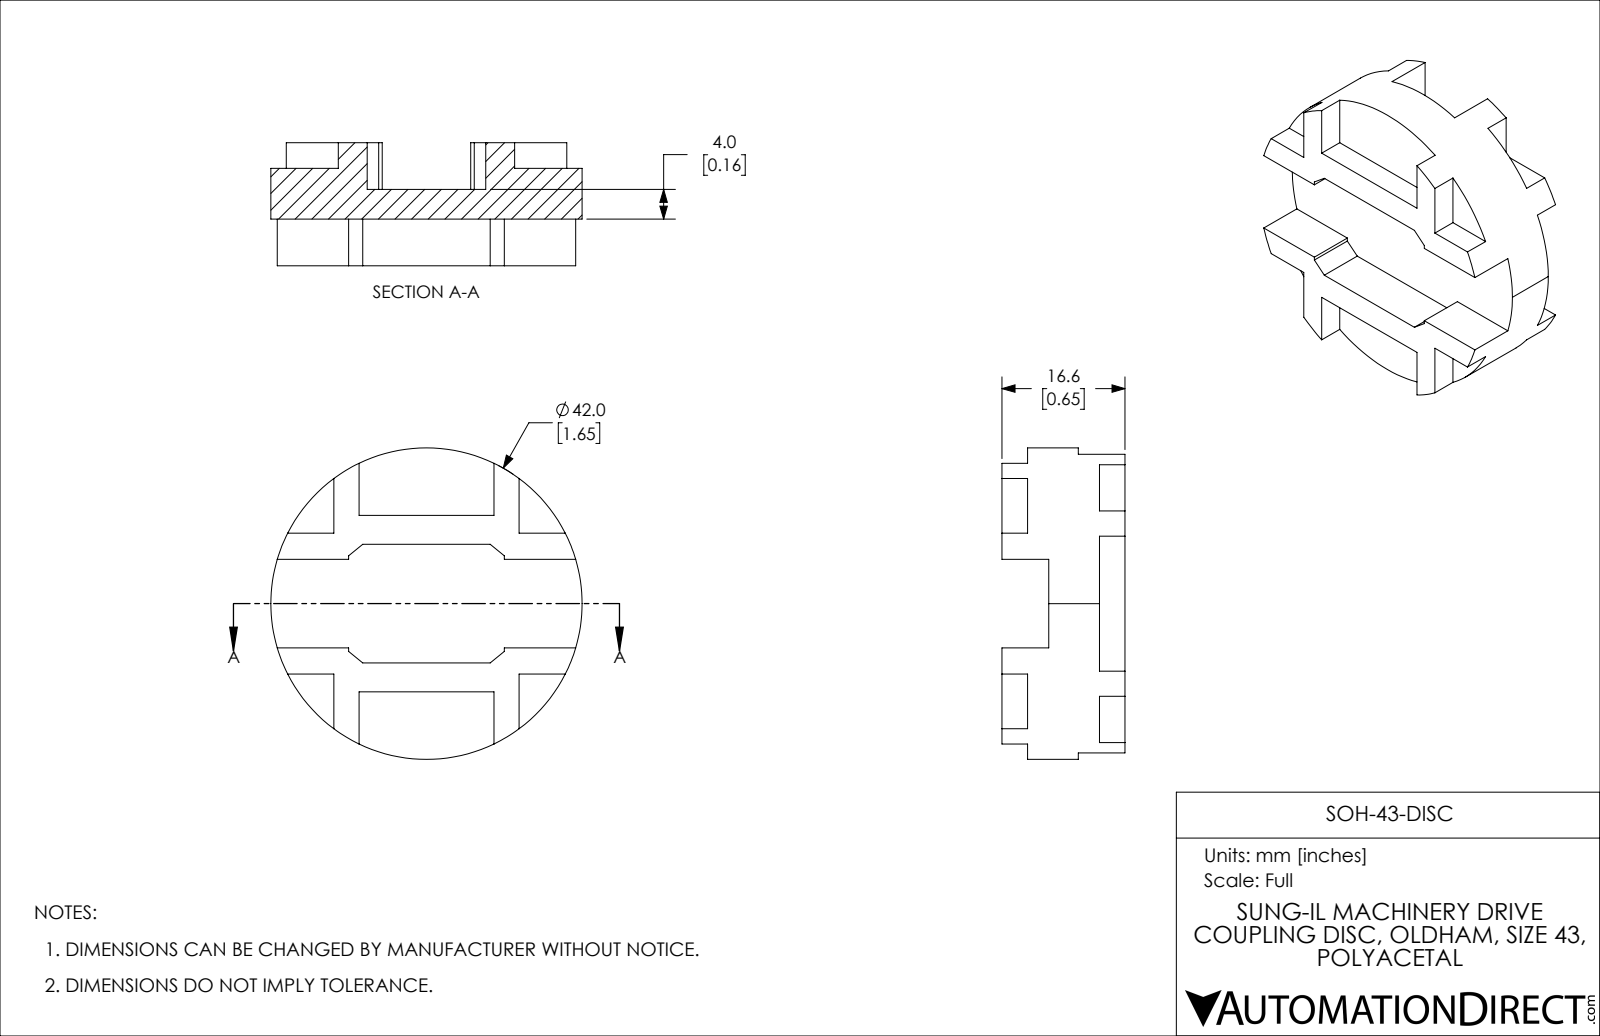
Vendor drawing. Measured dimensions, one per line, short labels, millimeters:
name: SOH-43-DISC
written by: SolidWorks 2021 (CONFIG_CONTROL_DESIGN)
unit: mm
bodies: 1 solid, 76 faces (74 planar, 2 cylindrical, 0 other)
size: 42 × 42 × 16.6
volume: 12 916 mm³; area: 6 015 mm²
bosses: 1× ⌀42
face distances: 2.85, 6.85, 3.45, 6.3, 10.3, 13.15, 4, 2.03, 13.97, 9.7
